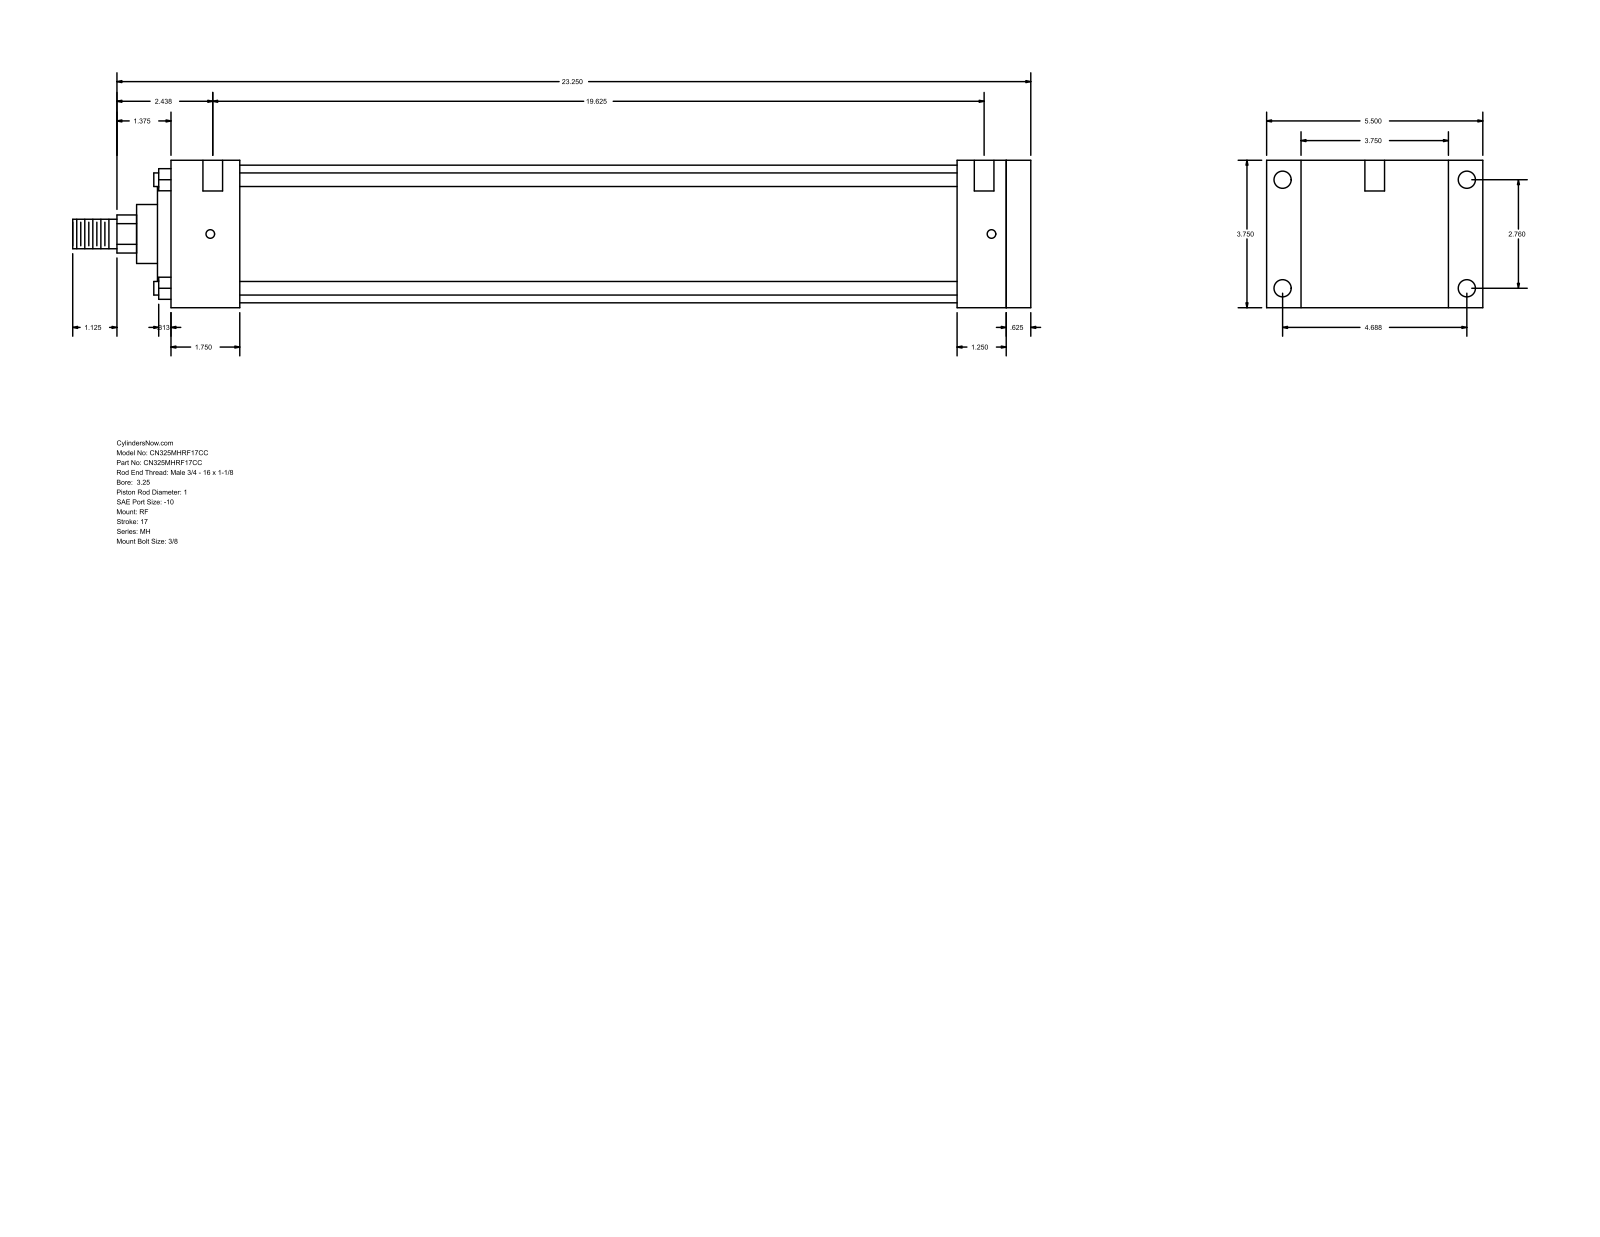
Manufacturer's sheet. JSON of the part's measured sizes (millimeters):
{"part_name": "MH_RF__0325_1", "step_written_by": "GSSL Pune (CONFIG_CONTROL_DESIGN)", "units": "millimeters", "bodies": {"solids": 0, "faces": 94, "planar": 65, "cylindrical": 29, "other": 0}, "overall_size": [619.12, 139.7, 95.25], "round_holes": [[5.56, 4], [11.13, 4], [12.7, 2]], "round_bosses_or_shafts": [[8.76, 4], [88.9, 1], [60.33, 1], [38.1, 1], [25.4, 1], [19.05, 1]], "partial_cylinders_radius": [[12.29, 1]], "face_to_face_distances": [95.24, 555.63, 539.75, 15.88, 22.23, 117.47, 44.46, 495.29, 511.17, 508], "hole_center_spacings": [70.1, 119.06, 138.16, 504.82, 1.58, 4.76, 498.48, 500.06]}
